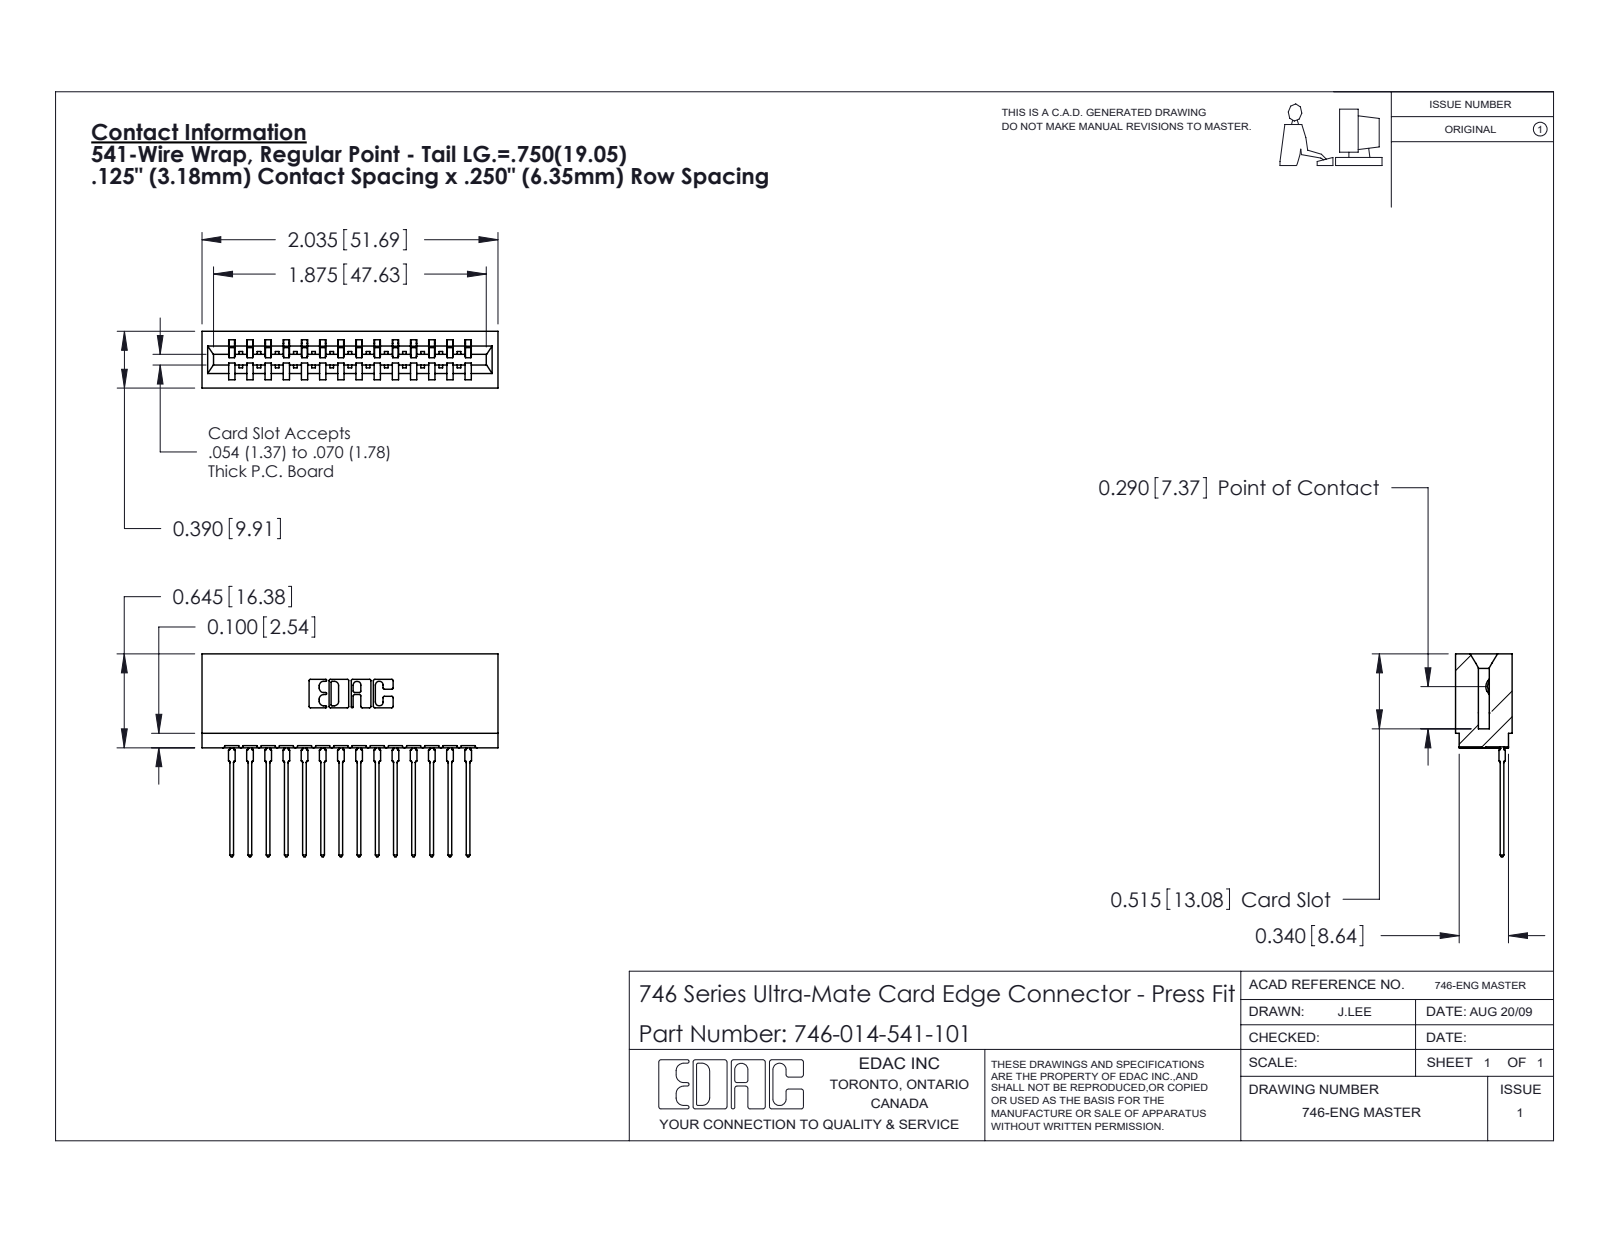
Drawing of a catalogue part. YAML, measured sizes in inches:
part_name: "746 Part_.515 Slot Depth - 01; 746-292-001_541; 746-014-541-101"
step_written_by: "SolidWorks 2020 (CONFIG_CONTROL_DESIGN)"
units: inches
bodies: {solids: 15, faces: 1609, planar: 937, cylindrical: 308, other: 364}
overall_size: [2.035, 1.394, 0.39]
volume: 0.345
surface_area: 12.79
partial_cylinders:
  - {radius: 0.021, count: 28}
  - {radius: 0.01, count: 22}
  - {radius: 0.015, count: 15}
  - {radius: 0.007, count: 6}
  - {radius: 0.031, count: 6}
  - {radius: 0.005, count: 4}
  - {radius: 0.011, count: 4}
  - {radius: 0.026, count: 3}
face_to_face_distances: [0.25, 0.333, 0.057, 0.5, 0.39, 0.042, 0.125, 0.083, 0.208, 0.125]
